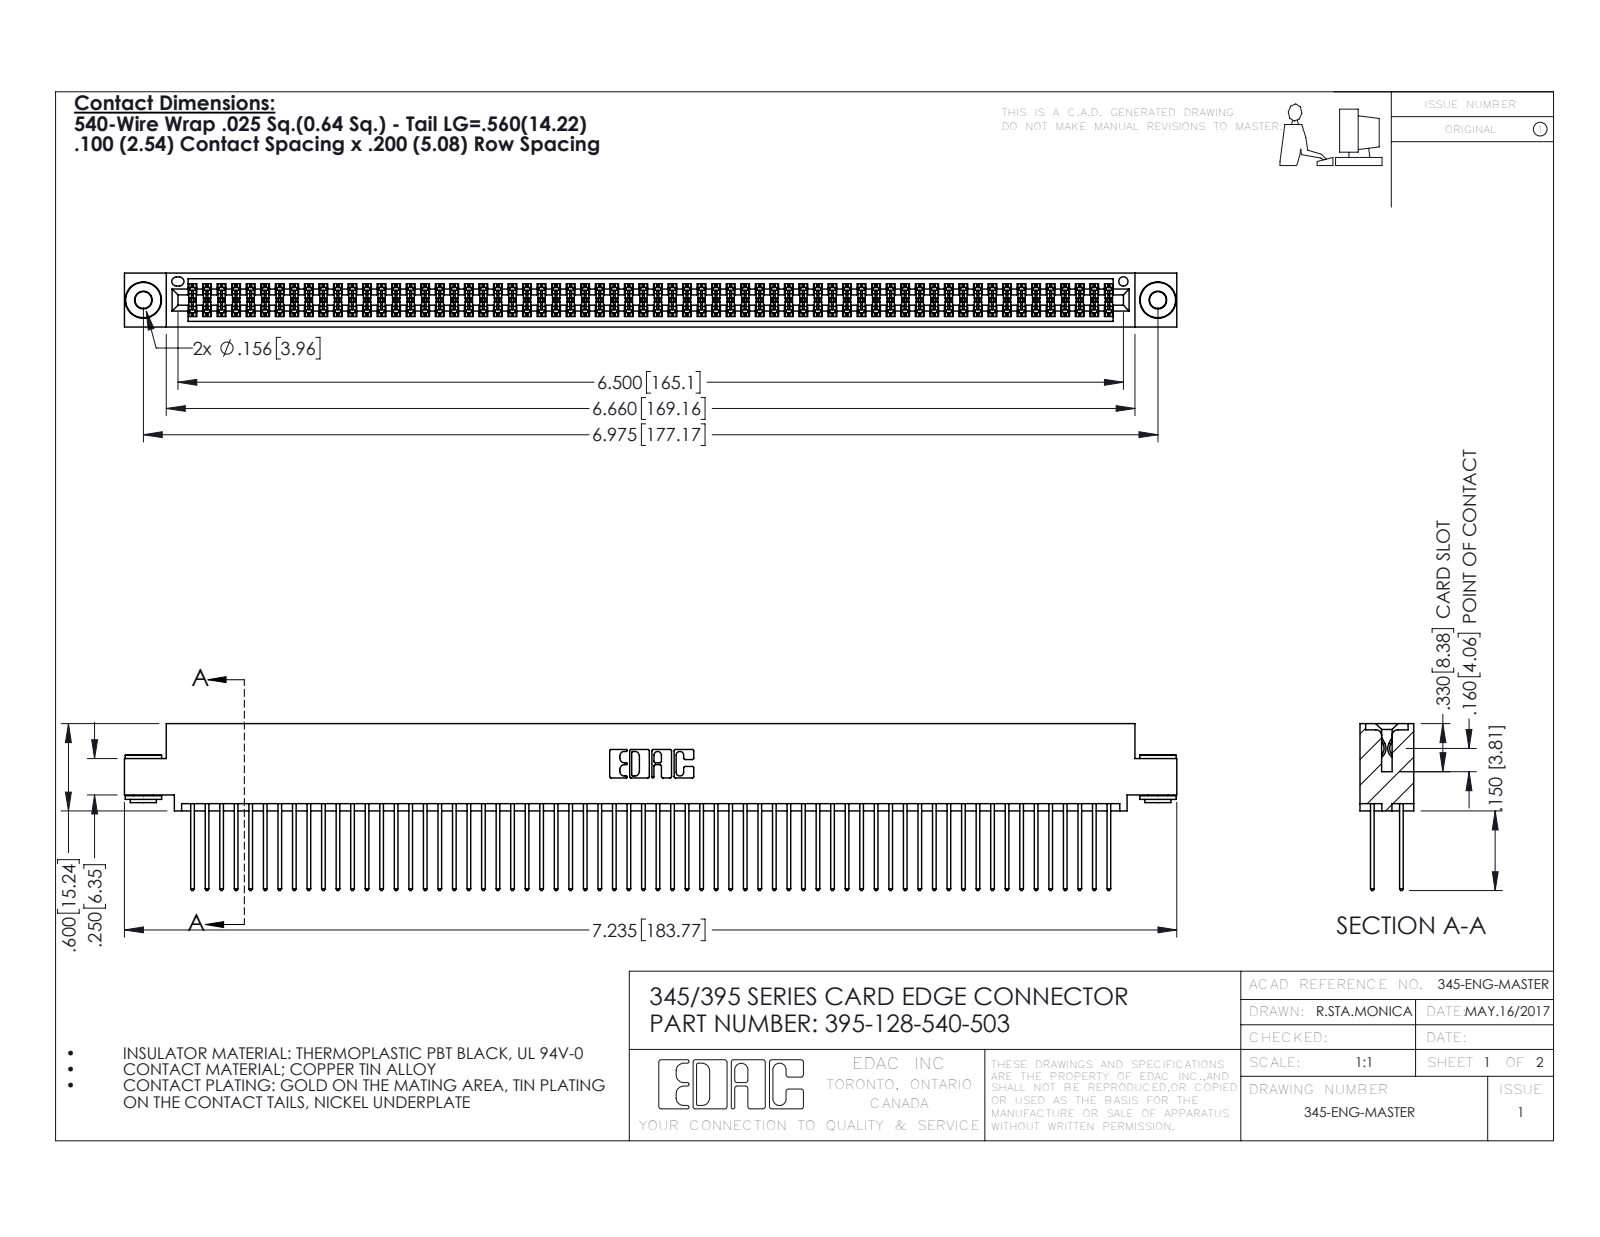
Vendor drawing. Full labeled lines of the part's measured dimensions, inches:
Part name (STEP PRODUCT): 345 Part_0.110 Offset - 0.156 Dia-TH; 345-292-001_345-293-140; 395-128-540-503; 345-250-002_345-250-002-102
STEP written by: SolidWorks 2016 (CONFIG_CONTROL_DESIGN)
Units: inches
Bodies: 131 solids, 6568 faces (4318 planar, 2242 cylindrical, 8 other)
Overall size (bounding box): 7.235 × 1.147 × 0.37
Volume: 1.128 in³ · Surface area: 46.97 in²
Round holes (diameter × count): ⌀0.116 ×2, ⌀0.156 ×2, ⌀0.064 ×1
Round bosses / shafts (diameter × count): ⌀0.25 ×2, ⌀0.18 ×2, ⌀0.136 ×2
Partial cylindrical surfaces — rounded edges, fillets, slot ends (radius × count): R0.006 ×192, R0.01 ×128, R0.01 ×22, R0.007 ×6, R0.031 ×6, R0.026 ×3, R0.014 ×2, R0.019 ×2
Main face-to-face distances: 0.072, 0.298, 0.2, 0.025, 0.098, 0.272, 0.225, 0.37, 0.175, 0.149
Hole centre spacings: 0.27, 6.739, 6.975
